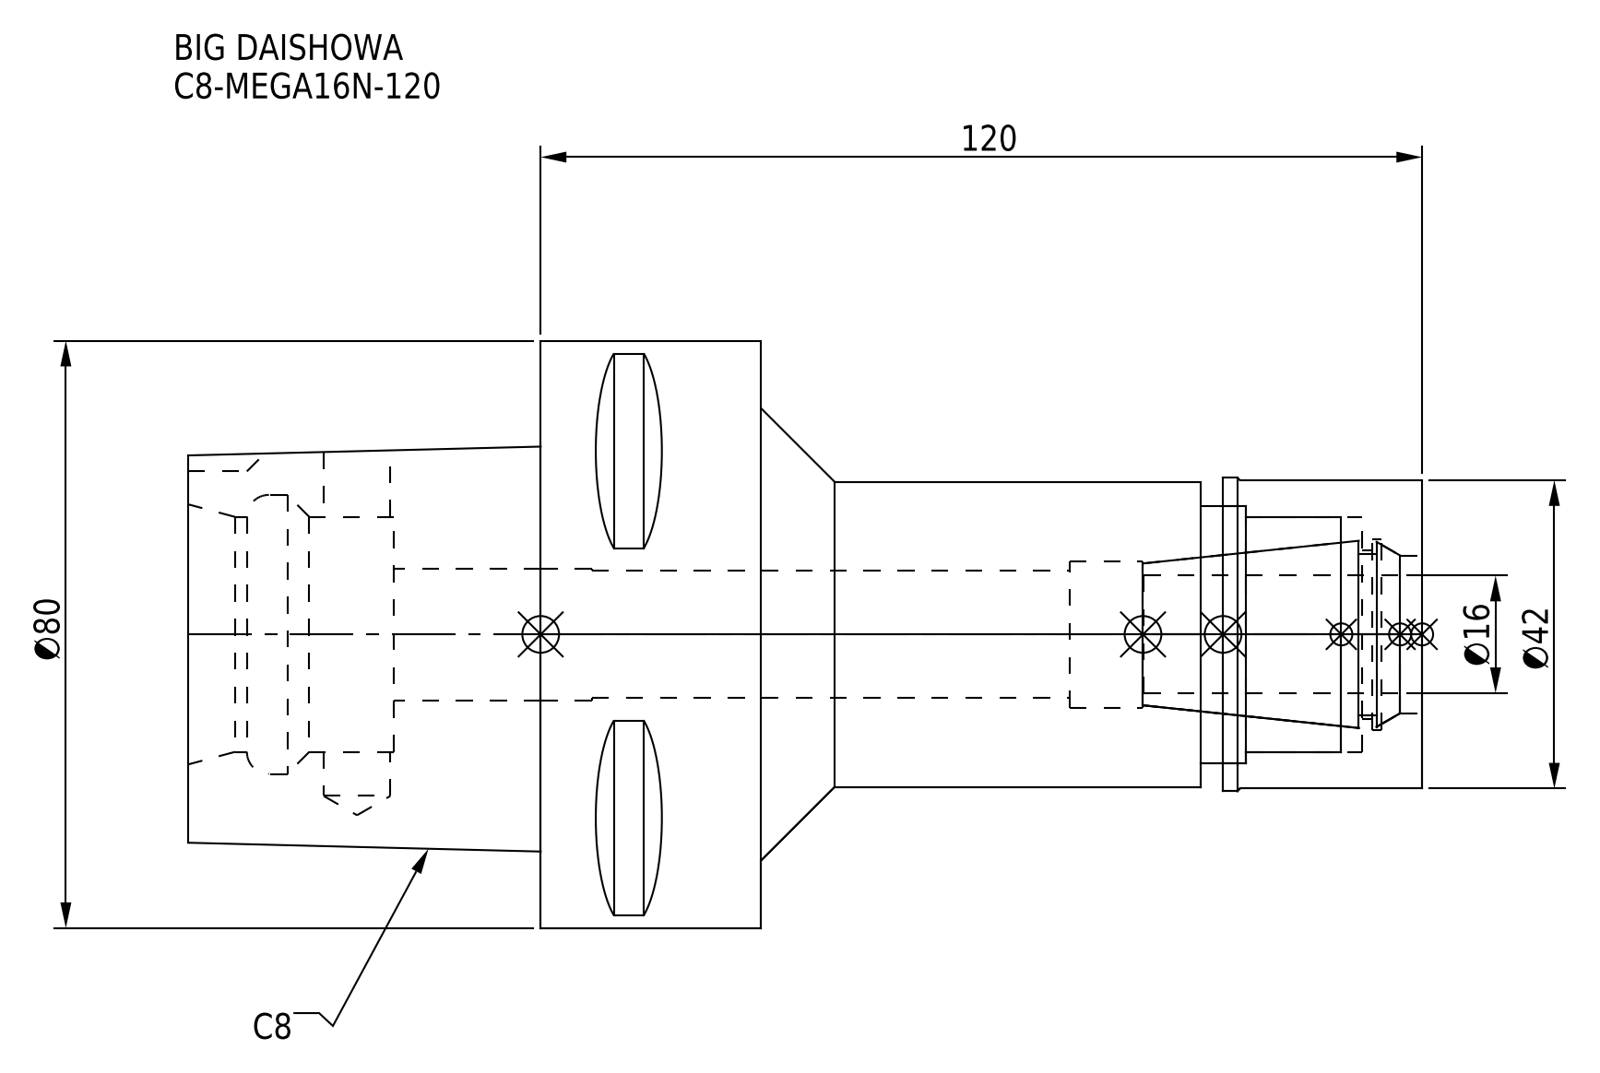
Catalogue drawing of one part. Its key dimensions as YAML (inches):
part_name: "C8-MEGA16N-120-160.stp; C8-MEGA16N-120; DXF_TEMP_ASSY_ASM_4_ASM.stp; MGN16_1.stp (+3 more)"
step_written_by: "SolidWorks 2019 (CONFIG_CONTROL_DESIGN)"
units: inches
bodies: {solids: 2, faces: 95, planar: 38, cylindrical: 39, other: 18}
overall_size: [6.614, 3.15, 3.15]
volume: 19.42
surface_area: 83.68
round_holes:
  - {diameter: 0.358, count: 1}
  - {diameter: 0.681, count: 1}
  - {diameter: 0.709, count: 1}
  - {diameter: 0.787, count: 1}
  - {diameter: 0.846, count: 1}
  - {diameter: 0.906, count: 1}
  - {diameter: 1.024, count: 1}
  - {diameter: 1.26, count: 1}
  - {diameter: 1.378, count: 1}
  - {diameter: 1.496, count: 1}
round_bosses_or_shafts:
  - {diameter: 3.15, count: 1}
  - {diameter: 1.681, count: 1}
  - {diameter: 1.654, count: 1}
  - {diameter: 1.638, count: 1}
partial_cylinders:
  - {radius: 0.236, count: 1}
face_to_face_distances: [1.181, 1.89, 4.724, 3.071, 3.543, 6.614, 0.787, 5.512, 1.969, 1.102]
